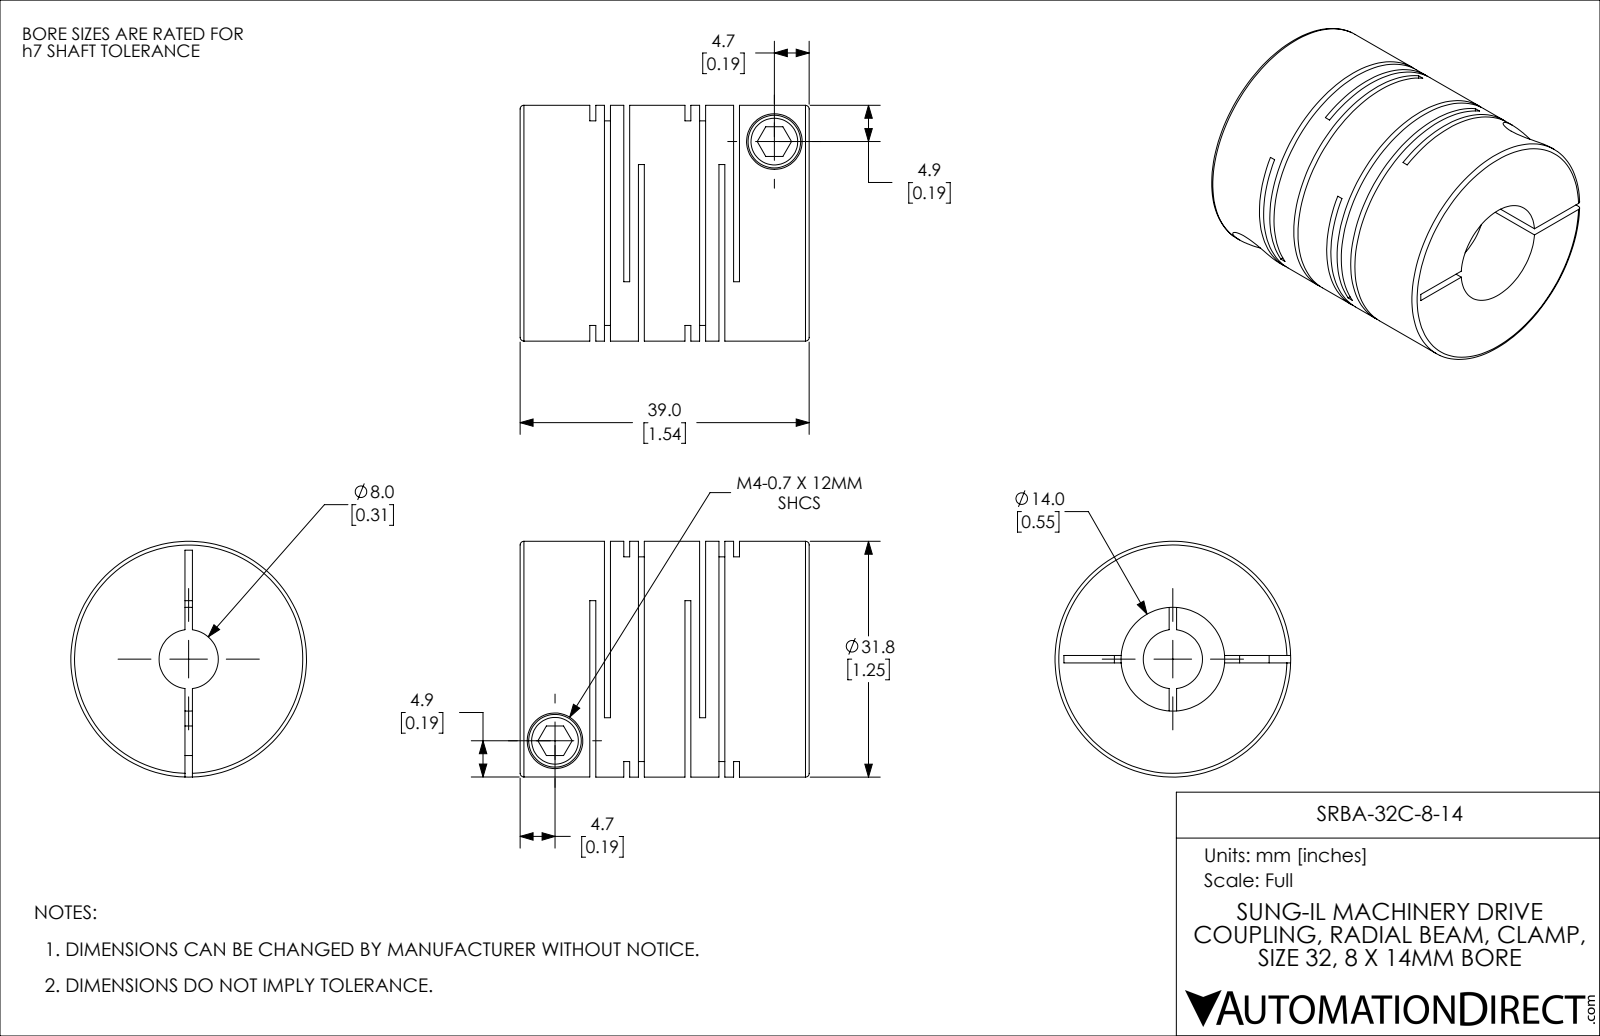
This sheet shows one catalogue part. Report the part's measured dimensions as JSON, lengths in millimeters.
{"part_name": "SRBA-32C-8-14", "step_written_by": "SolidWorks 2021 (CONFIG_CONTROL_DESIGN)", "units": "millimeters", "bodies": {"solids": 1, "faces": 114, "planar": 60, "cylindrical": 42, "other": 12}, "overall_size": [39, 31.8, 31.8], "volume_mm3": 21985, "surface_area_mm2": 15257, "round_holes": [[4, 2], [7.5, 2], [8, 1], [14, 1]], "round_bosses_or_shafts": [[7.1, 2], [31.8, 1]], "face_to_face_distances": [0.8, 12.84, 1.98, 4.58, 12.04, 1.18, 10.86, 3.78, 8.26, 2.6]}
